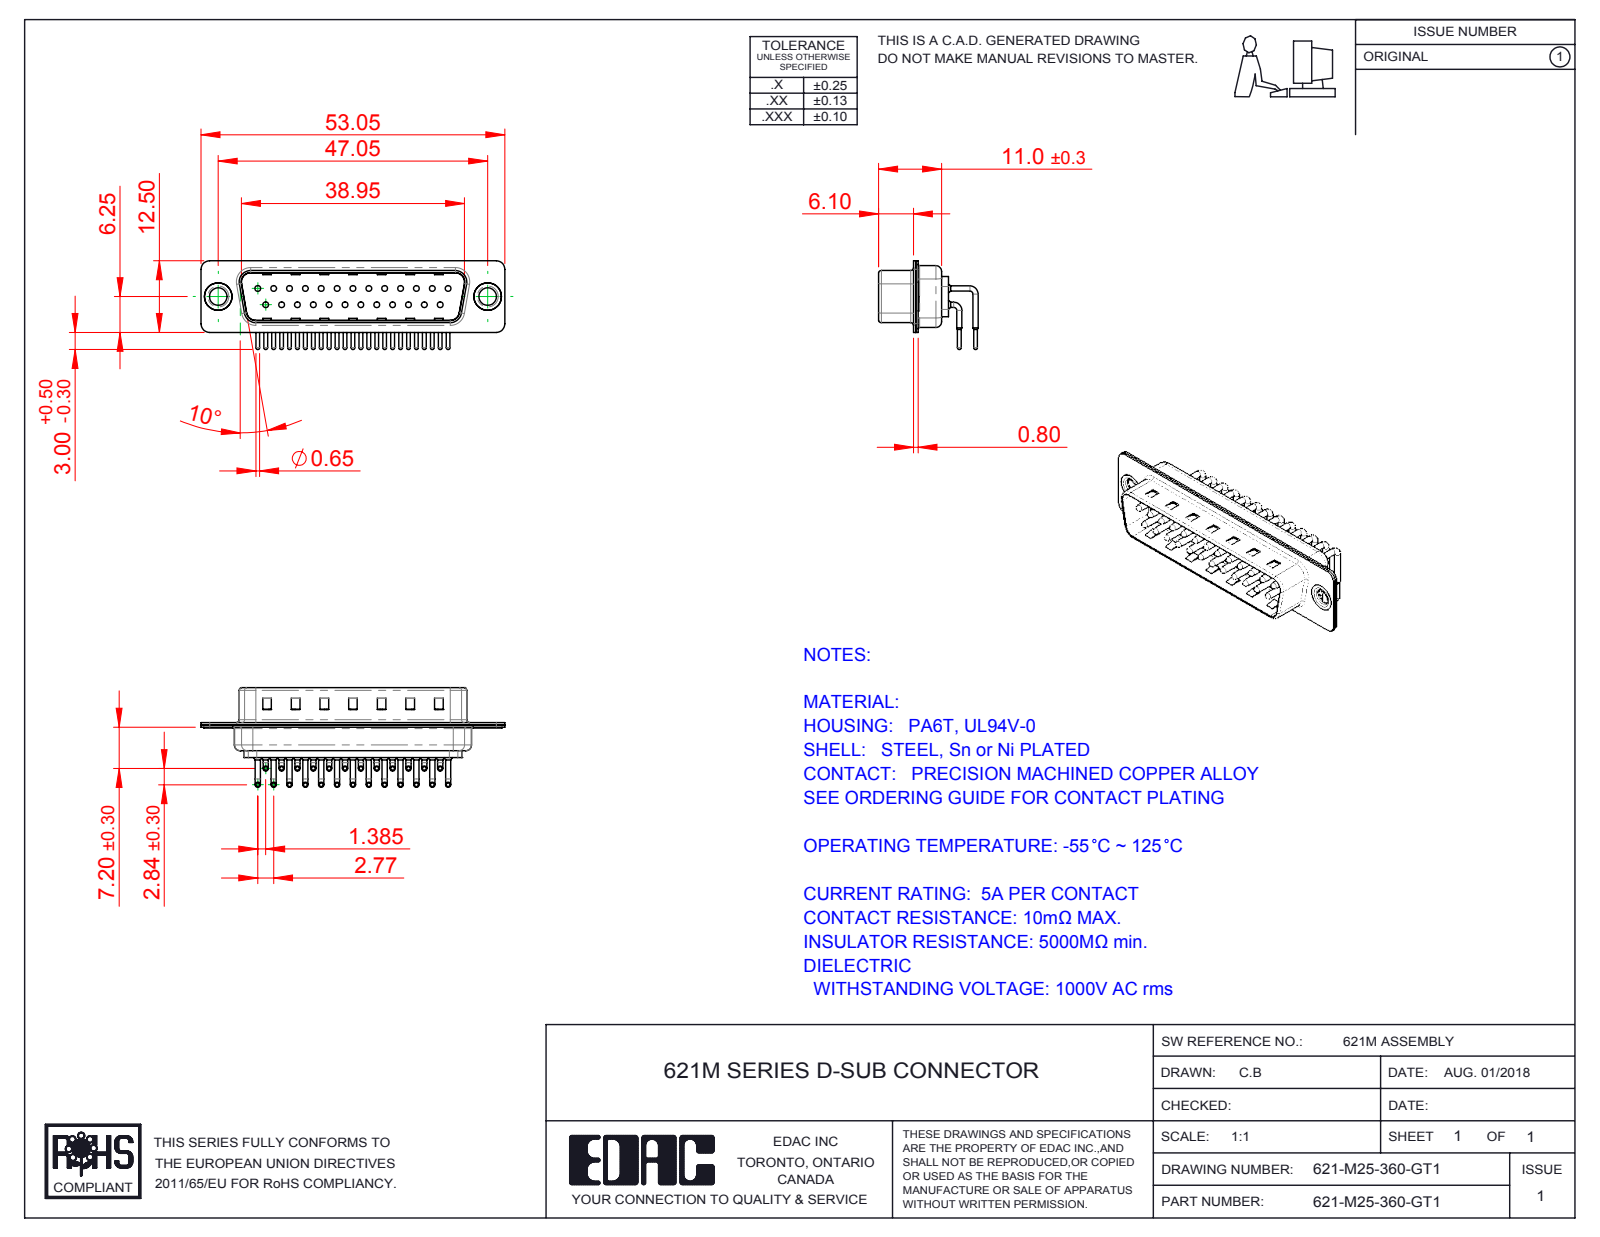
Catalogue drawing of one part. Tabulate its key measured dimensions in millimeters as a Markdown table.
| quantity | value |
| --- | --- |
| part name | 621M Contact Row 2; 621M Shell Front_25 Contacts; 621-M25-360-GT1; 621M Thru Hole Rivet (+3 more) |
| STEP written by | SolidWorks 2016 (CONFIG_CONTROL_DESIGN) |
| units | millimeters |
| bodies | 30 solids, 3100 faces (1771 planar, 1021 cylindrical, 308 other) |
| overall size | 53.05 × 17.39 × 15.49 |
| volume | 2 796 mm³ |
| surface area | 7 439 mm² |
| round holes (diameter × count) | 1 × 25, 1.7 × 25, 2 × 25, 3.05 × 2, 4 × 2, 4.8 × 2 |
| round bosses / shafts (diameter × count) | 0.9 × 50, 1.5 × 25, 0.65 × 25, 5 × 2, 4.9 × 2, 3.55 × 2 |
| partial cylindrical surfaces (radius × count) | 1.01 × 25, 1.5 × 16, 2 × 12, 0.5 × 8, 1.6 × 8, 0.25 × 4, 0.6 × 4, 0.65 × 4 |
| main face-to-face distances | 0.4, 0.85, 9.55, 8.7, 1.25, 10.4, 1.5, 1.9, 0.35, 6.1 |
| hole center spacings | 3.16, 8.31, 2.77, 5.54, 11.08, 16.62, 5.03, 5.04 |
